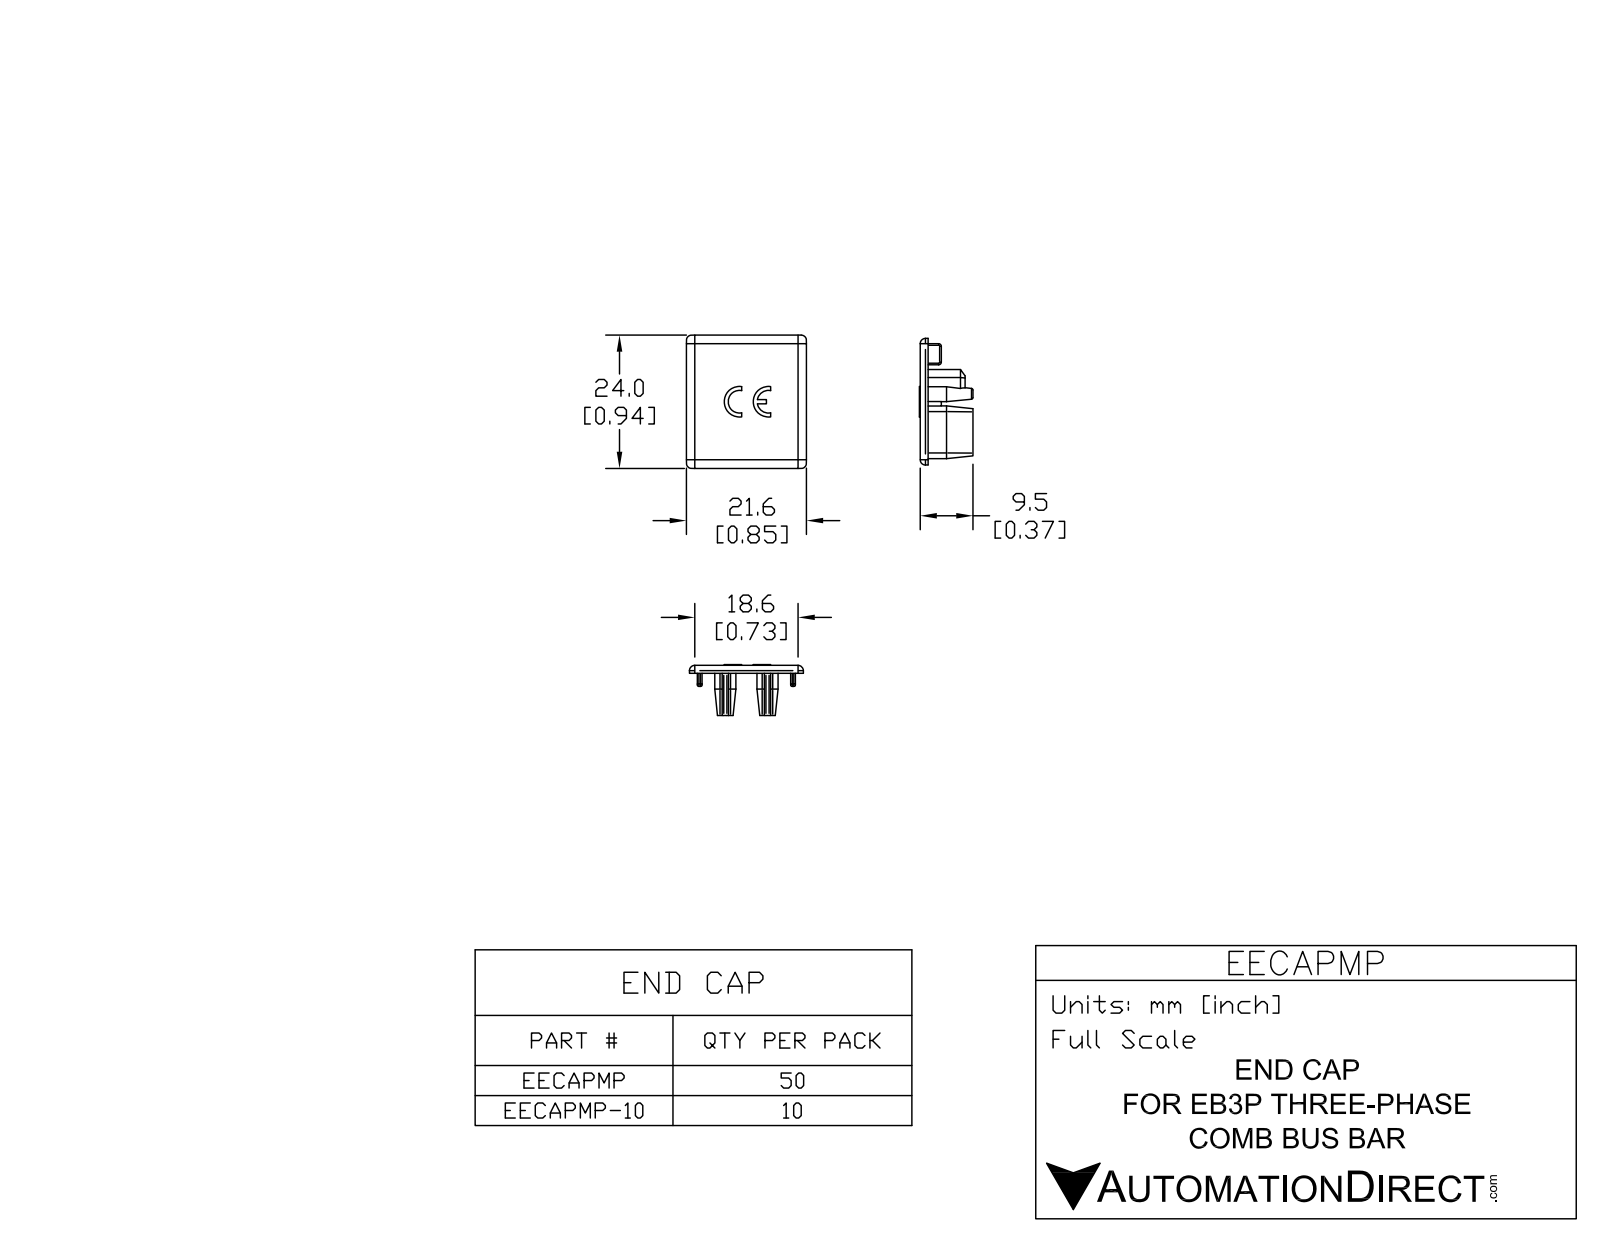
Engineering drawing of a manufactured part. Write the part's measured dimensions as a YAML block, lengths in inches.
part_name: "EECAPMP"
step_written_by: "SolidWorks 2011 (AUTOMOTIVE_DESIGN)"
units: inches
bodies: {solids: 2, faces: 77, planar: 51, cylindrical: 18, other: 8}
overall_size: [0.94, 0.85, 0.375]
volume: 0.076
surface_area: 2.915
partial_cylinders:
  - {radius: 0.03, count: 14}
face_to_face_distances: [0.06, 0.284, 0.286, 0.047, 0.315, 0.375, 0.333, 0.285, 0.665, 0.239]
